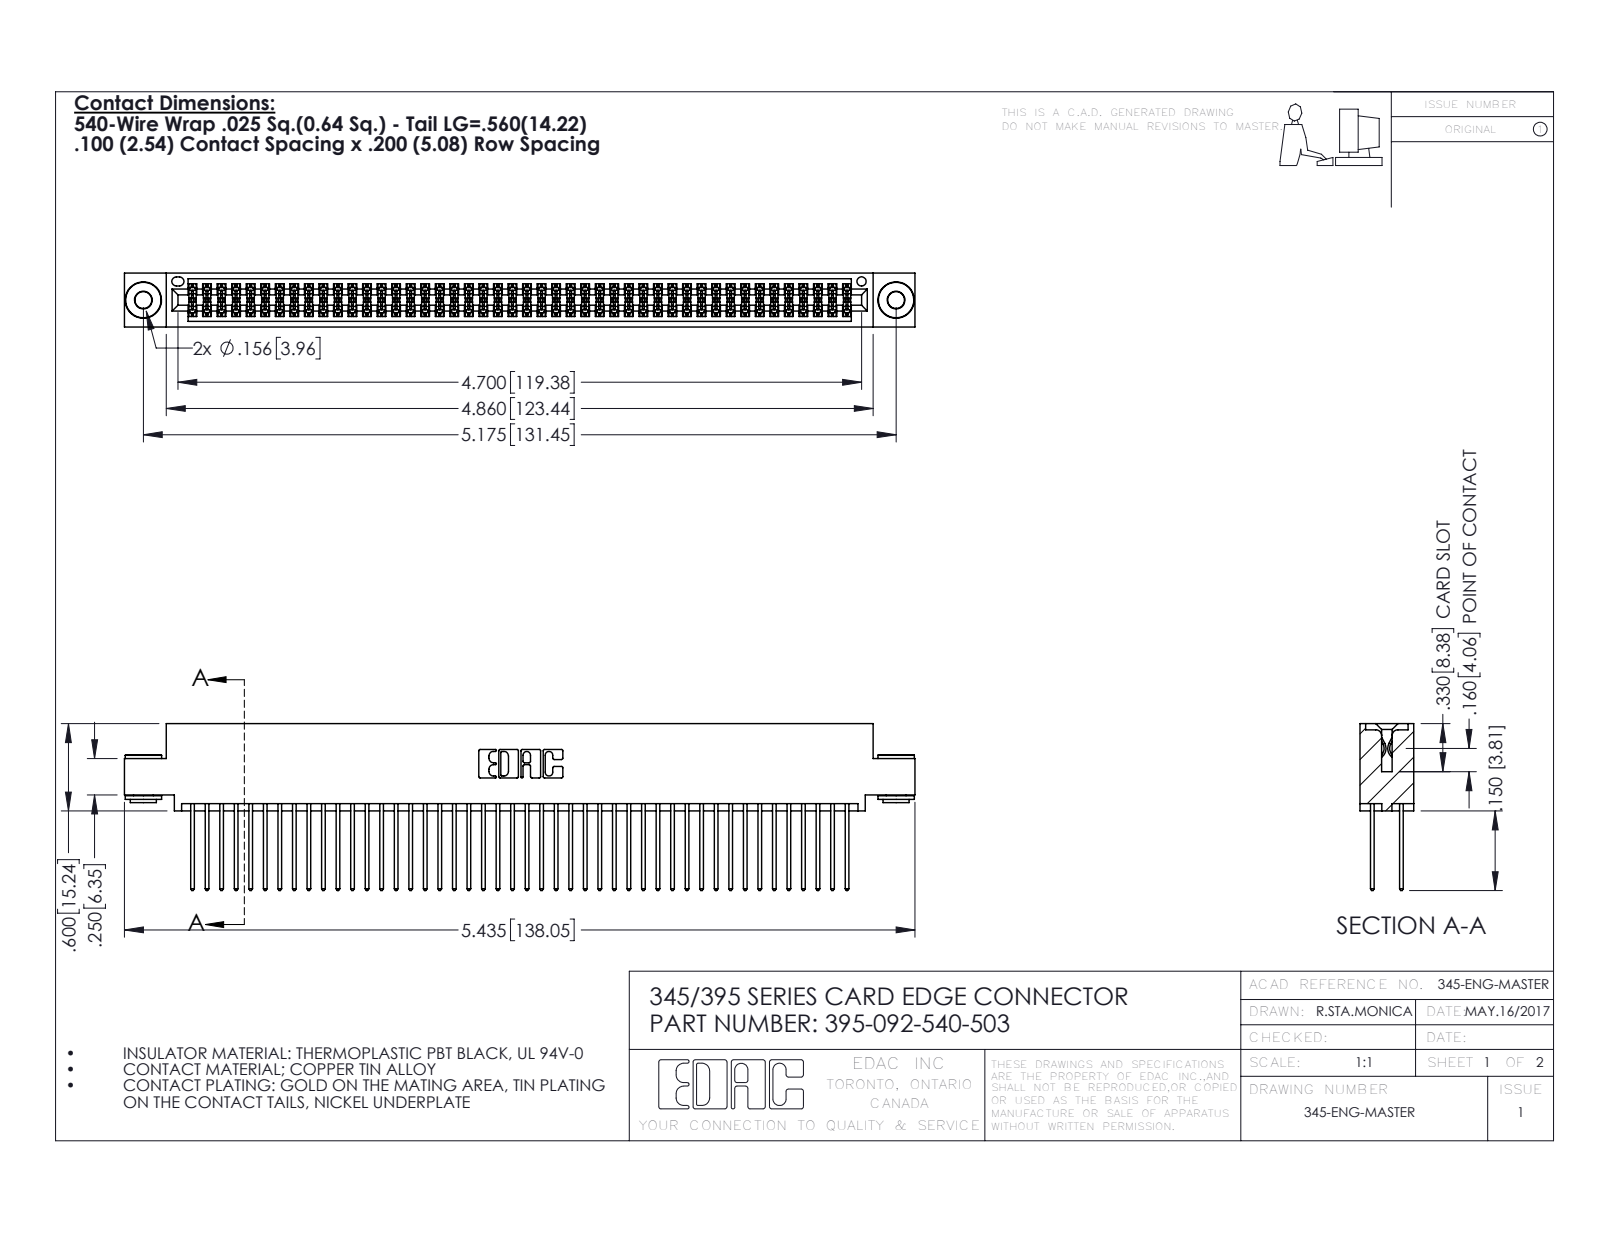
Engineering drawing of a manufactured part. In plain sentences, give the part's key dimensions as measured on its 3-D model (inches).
The part is named "345-292-001_345-293-140; 345 Part_0.110 Offset - 0.156 Dia-TH; 395-092-540-503; 345-250-002_345-250-002-102". Its 3-D file was written by "SolidWorks 2016 (CONFIG_CONTROL_DESIGN)". It is 95 solids with 4768 faces: 3130 planar, 1630 cylindrical and 8 other. Overall it measures 5.435 by 1.147 by 0.37 inches. Its volume is 0.839 cubic inches and its surface area 34.58 square inches. Round holes: 2 of diameter 0.116, 2 of diameter 0.156, 1 of diameter 0.064. Round bosses or shafts: 2 of diameter 0.25, 2 of diameter 0.18, 2 of diameter 0.136. Partial cylindrical surfaces (rounded edges, fillets, slot ends): 138 of radius 0.006, 92 of radius 0.01, 22 of radius 0.01, 6 of radius 0.007, 6 of radius 0.031, 3 of radius 0.026, 2 of radius 0.014, 2 of radius 0.019. The main face-to-face distances are 0.072, 0.298, 0.2, 0.025, 0.098, 0.272, 0.37, 0.225, 0.175, 0.149. The hole center spacings are 0.27, 4.939, 5.175.
